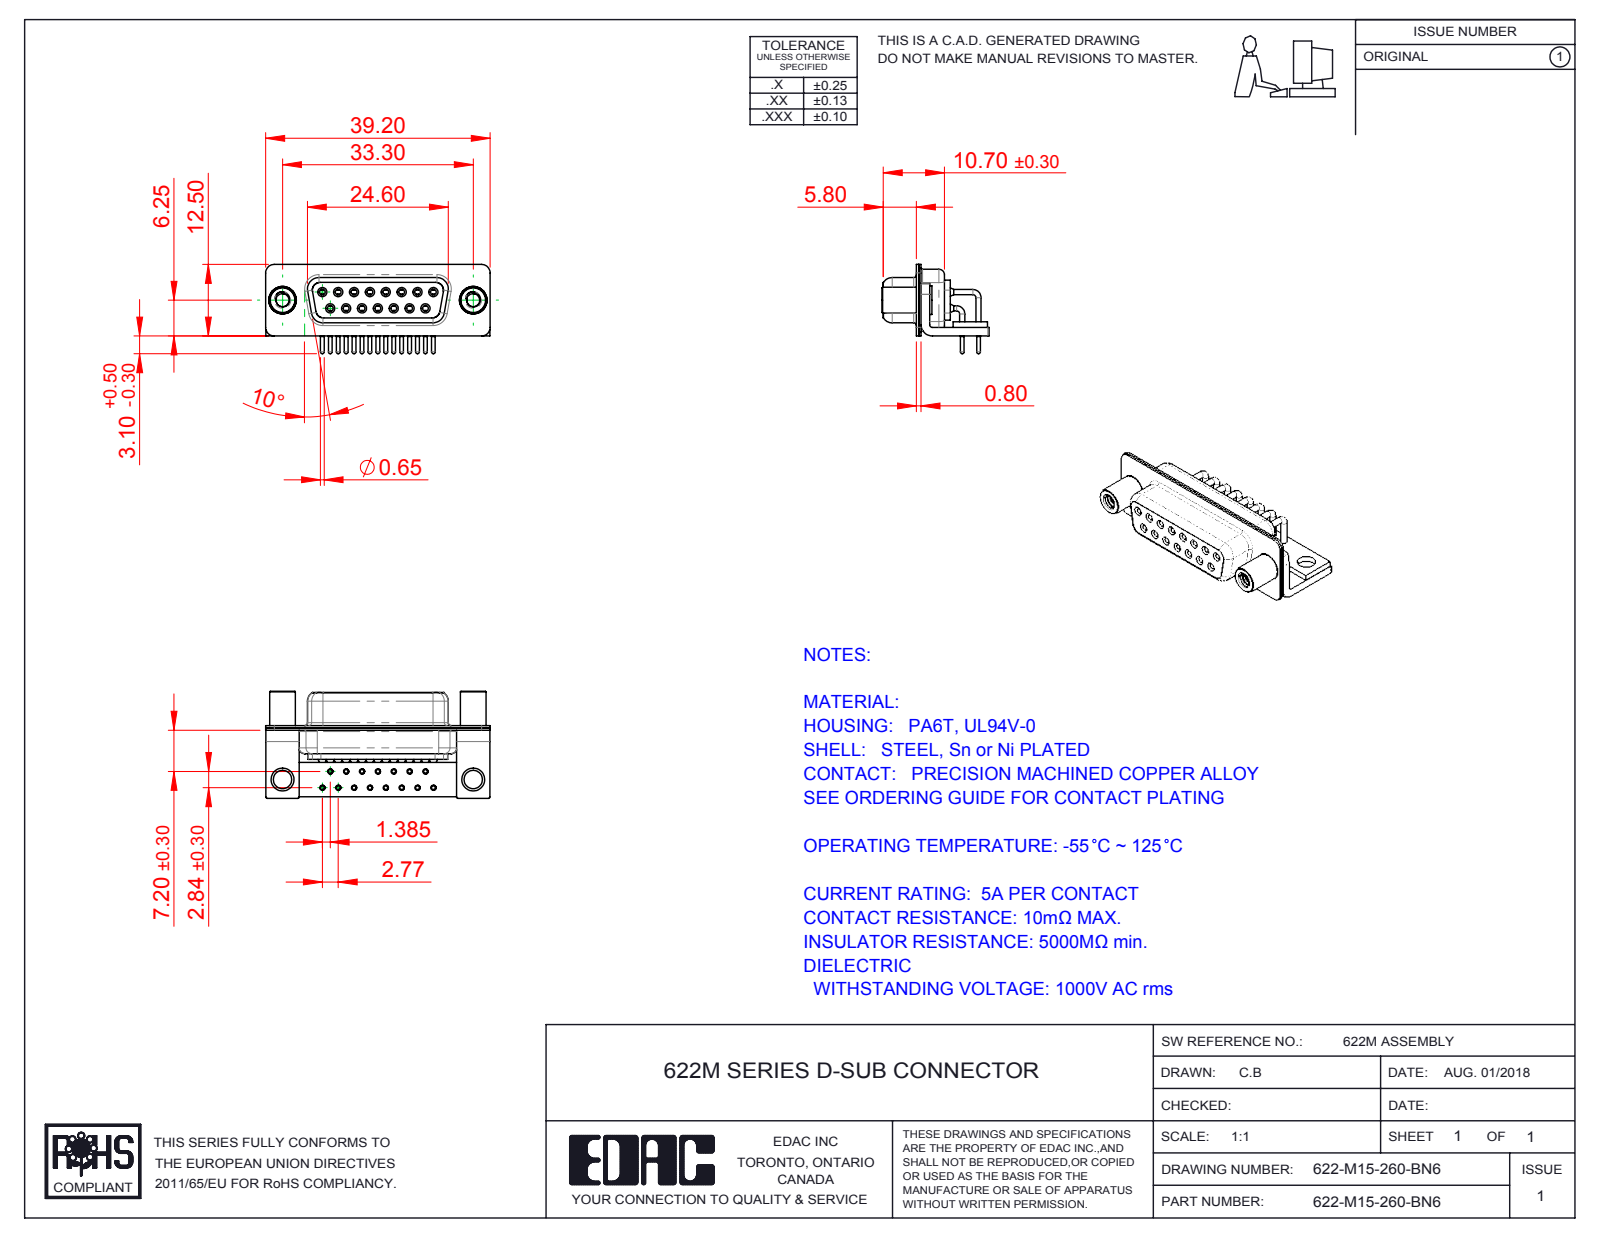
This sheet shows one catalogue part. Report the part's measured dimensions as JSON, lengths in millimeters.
{"part_name": "622M Contact Row 2; 622M Contact Row 1; 622M Shell Rear_15 Contacts; 622M Shell Front_15 Contacts (+5 more)", "step_written_by": "SolidWorks 2016 (CONFIG_CONTROL_DESIGN)", "units": "millimeters", "bodies": {"solids": 23, "faces": 1204, "planar": 320, "cylindrical": 576, "other": 308}, "overall_size": [39.2, 18.7, 15.6], "volume_mm3": 3100, "surface_area_mm2": 7827, "round_holes": [[0.9, 15], [1, 15], [1.1, 15], [1.7, 15], [1.8, 15], [2, 15], [2.26, 2], [3.2, 2], [4, 2], [4.8, 2]], "round_bosses_or_shafts": [[0.9, 22], [1.6, 15], [1.5, 15], [0.65, 15], [5, 2], [4.9, 2], [4.5, 2]], "partial_cylinders_radius": [[0.25, 16], [1.5, 16], [2, 13], [1.35, 8], [1.6, 8], [0.5, 5], [0.6, 4], [0.65, 4]], "face_to_face_distances": [0.4, 2.3, 1.9, 0.8, 9.35, 1.5, 1, 1.45, 8.95, 0.85], "hole_center_spacings": [3.16, 2.77, 5.54, 8.31, 11.08, 5.03, 5.04, 7.48]}
